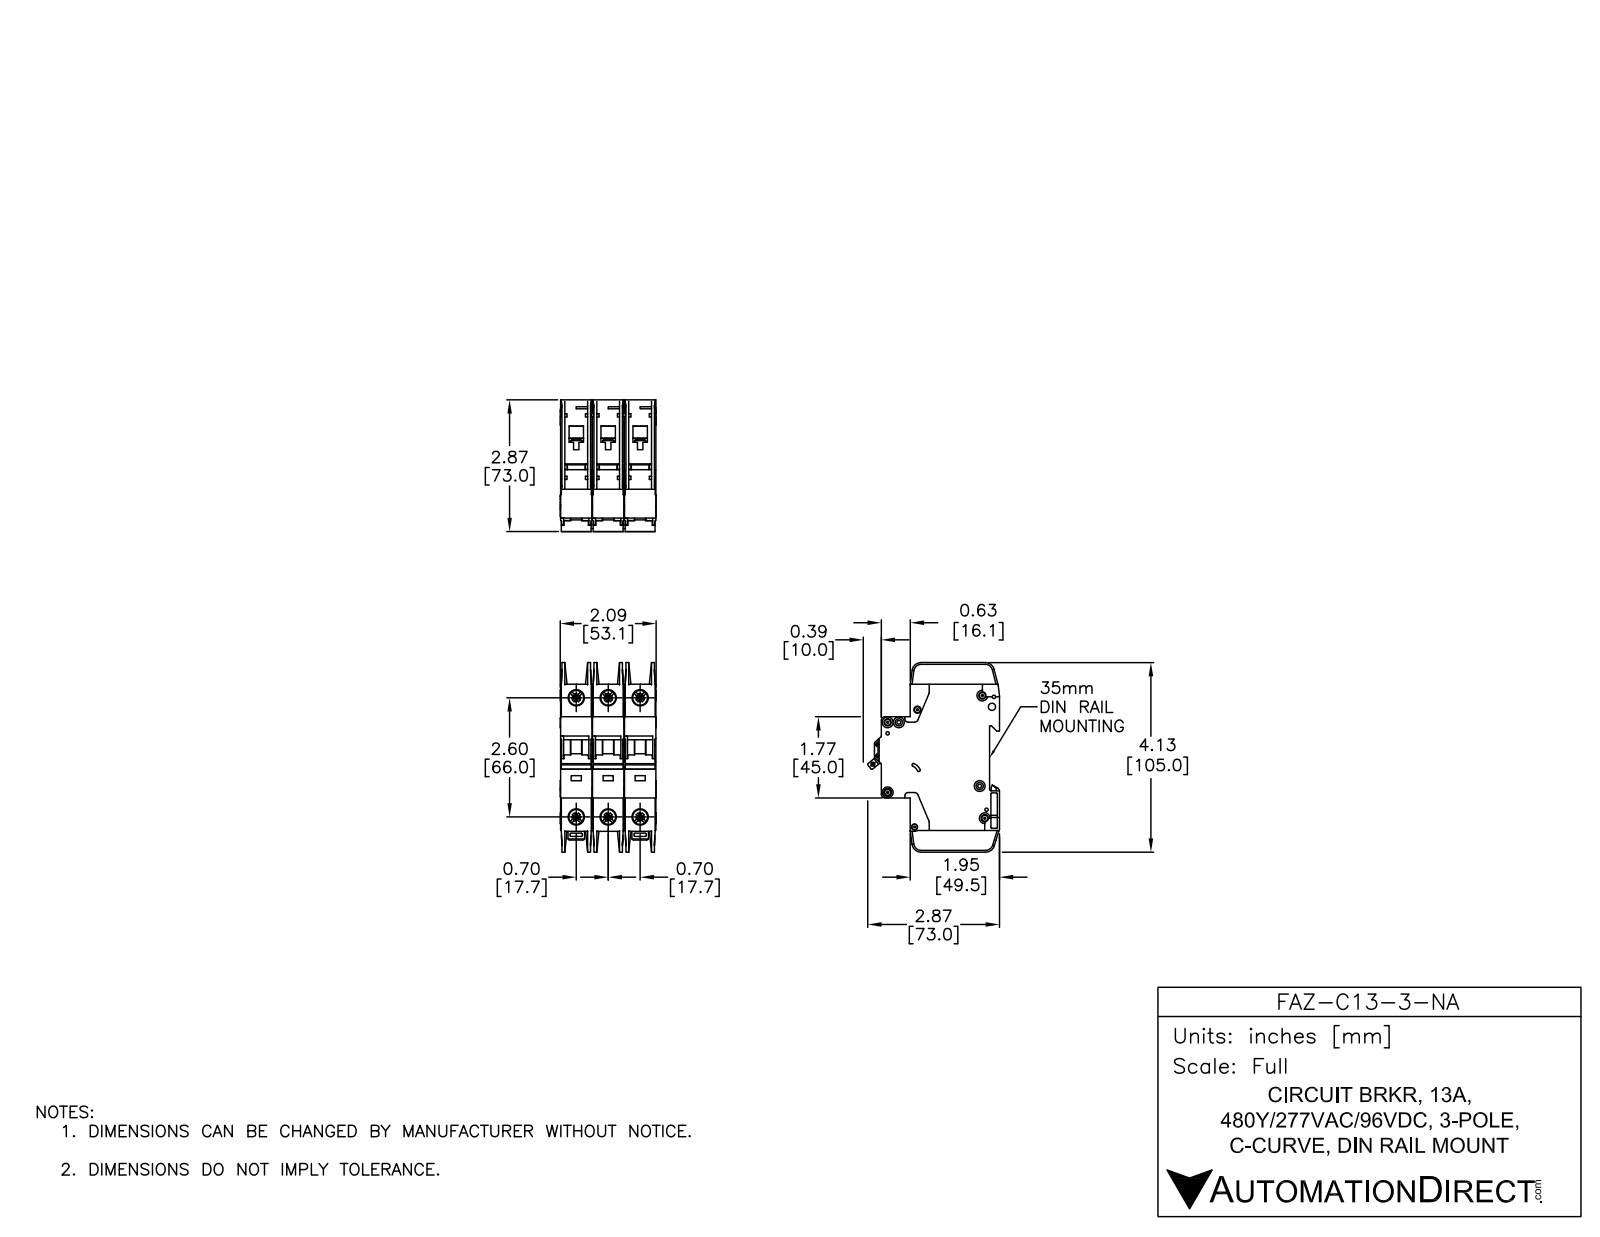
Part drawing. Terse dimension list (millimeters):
name: FAZ-C13-3-NA
written by: SolidWorks 2014 (AUTOMOTIVE_DESIGN)
unit: mm
bodies: 9 solids, 2352 faces (1227 planar, 789 cylindrical, 336 other)
size: 105 × 73.04 × 53.1
volume: 233 085 mm³; area: 74 219 mm²
holes: 7× ⌀3.6, 6× ⌀7.15, 6× ⌀8.2, 2× ⌀1.09, 2× ⌀1.5, 2× ⌀4, 1× ⌀1.9, 1× ⌀2.15, 1× ⌀2.2, 1× ⌀2.55, 1× ⌀3.3, 1× ⌀3.4
bosses: 7× ⌀6, 3× ⌀2.5
rounds: 65× R0.25, 30× R0.5, 26× R1, 14× R2, 5× R1.8, 5× R5, 4× R4, 2× R0.2
face distances: 17.7, 35.4, 17.5, 35.2, 0.7, 15.05, 2.45, 1.75, 15.75, 13.3
hole spacings: 17.7, 68.33, 66, 6.2, 35.4, 74.89, 5.19, 6.1
